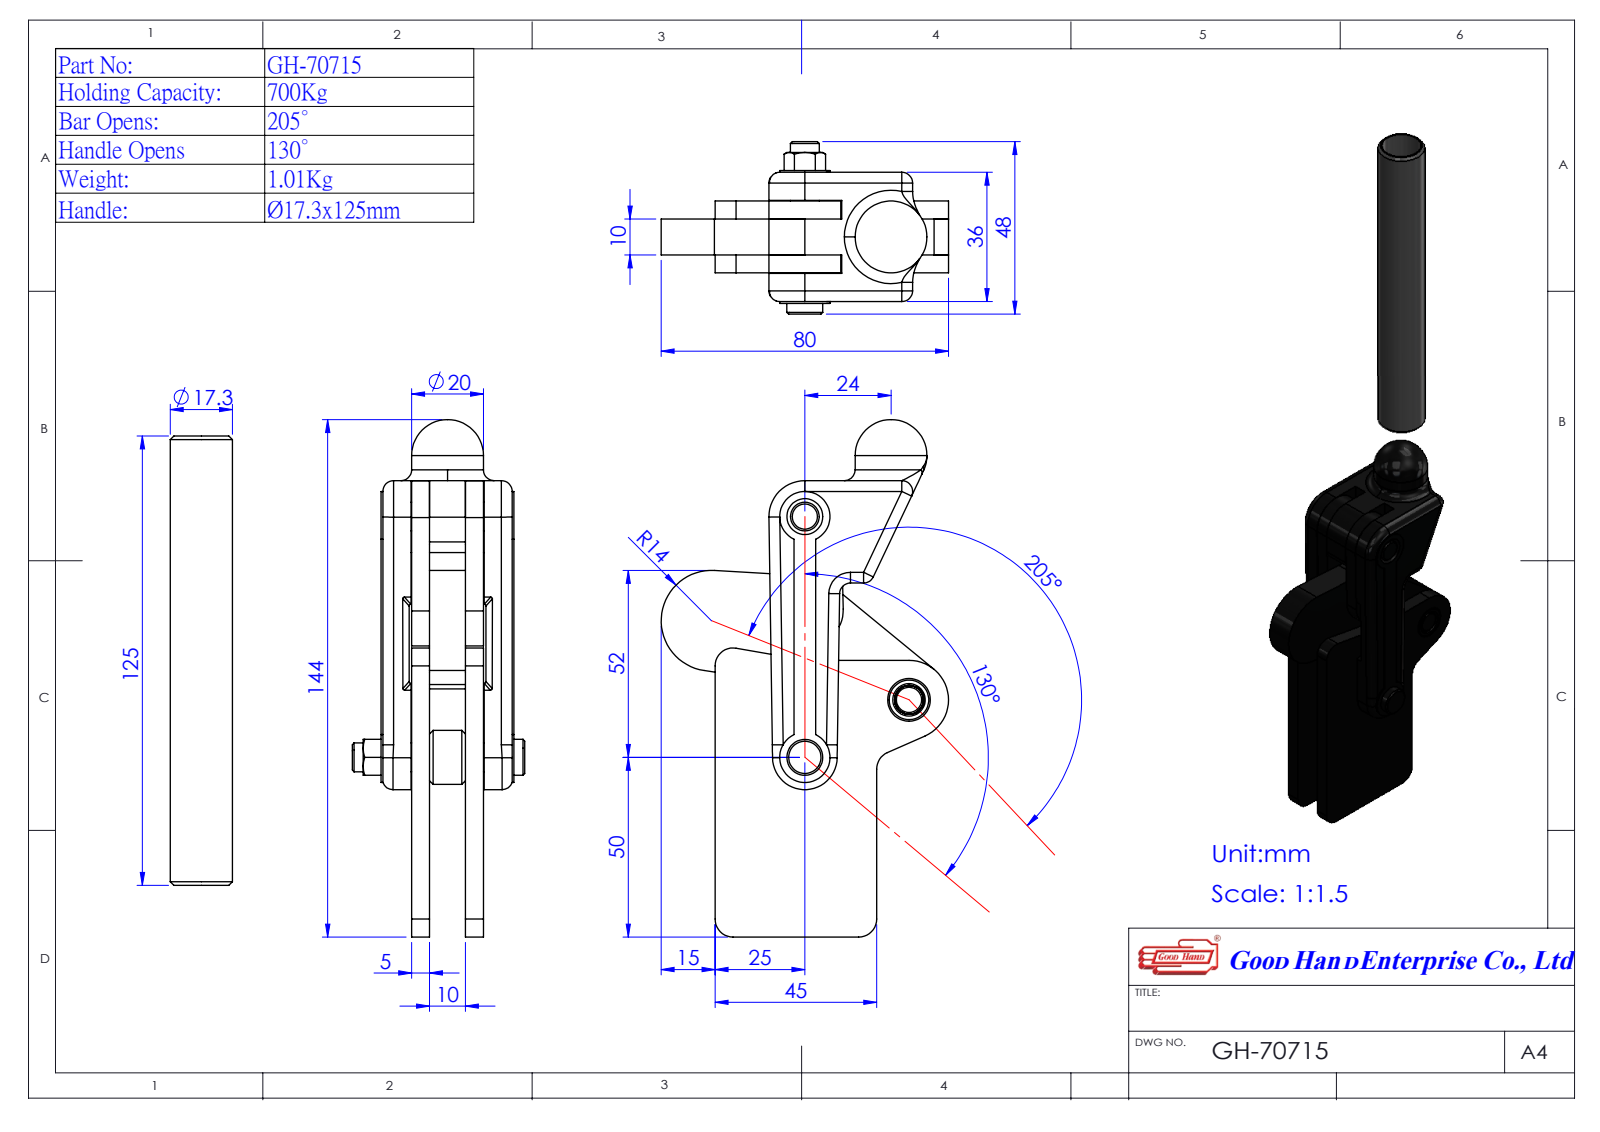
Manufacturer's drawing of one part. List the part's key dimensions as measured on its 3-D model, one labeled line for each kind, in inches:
Part name (STEP PRODUCT): 17030501-1-1^GH-70715(簡化)-1; 4702008-1^GH-70715(簡化)-1; GH-70715(簡化)-1; Group5^GH-70715(簡化)-1 (+2 more)
STEP written by: SolidWorks 2016 (AUTOMOTIVE_DESIGN)
Units: inches
Bodies: 5 solids, 200 faces (74 planar, 89 cylindrical, 37 other)
Overall size (bounding box): 10.619 × 3.17 × 1.831
Volume: 7.999 in³ · Surface area: 87.32 in²
Round holes (diameter × count): ⌀0.236 ×4, ⌀0.492 ×1
Round bosses / shafts (diameter × count): ⌀0.551 ×2, ⌀0.787 ×1, ⌀0.689 ×1, ⌀0.394 ×1
Partial cylindrical surfaces — rounded edges, fillets, slot ends (radius × count): R0.118 ×14, R0.197 ×4, R0.394 ×4, R0.354 ×1, R0.433 ×1, R0.433 ×1, R0.44 ×1, R0.572 ×1
Main face-to-face distances: 0.591, 0.197, 0.394, 0.787, 0.203, 0.596, 0.793, 0.799, 0.512, 0.309
Hole centre spacings: 1.024, 1.304, 1.487, 1.615, 2.314, 2.638
